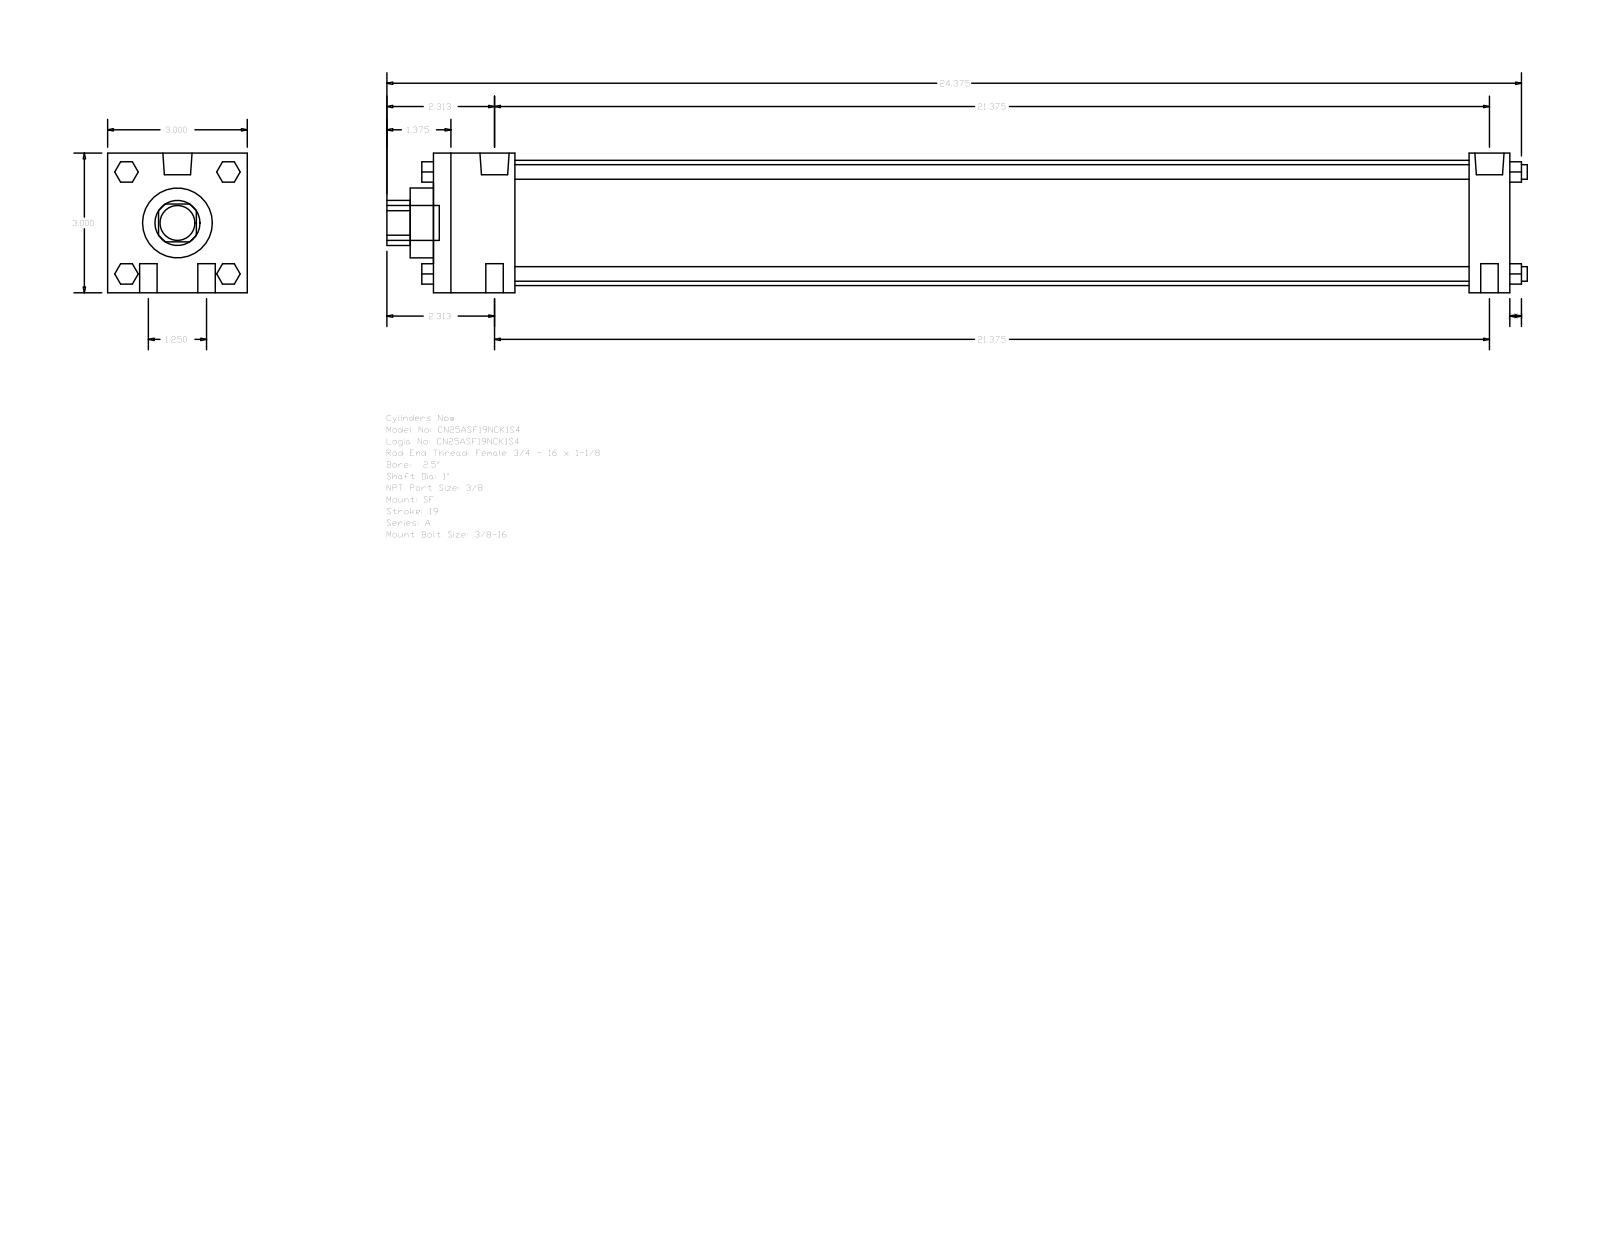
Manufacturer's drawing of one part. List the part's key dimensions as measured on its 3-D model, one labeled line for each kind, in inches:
Part name (STEP PRODUCT): A_SF__0250_1
STEP written by: GSSL Pune (CONFIG_CONTROL_DESIGN)
Units: inches
Bodies: 0 solids, 124 faces (94 planar, 30 cylindrical, 0 other)
Overall size (bounding box): 24.5 × 3 × 3
Round holes (diameter × count): ⌀1 ×1, ⌀1.5 ×1, ⌀2.69 ×1
Round bosses / shafts (diameter × count): ⌀0.375 ×4, ⌀0.313 ×4, ⌀0.627 ×2, ⌀0.219 ×2, ⌀0.75 ×1
Partial cylindrical surfaces — rounded edges, fillets, slot ends (radius × count): R0.484 ×1
Main face-to-face distances: 3, 23.125, 22.25, 0.875, 1.75, 20.5, 21.375, 0.5, 23.625, 0.25
